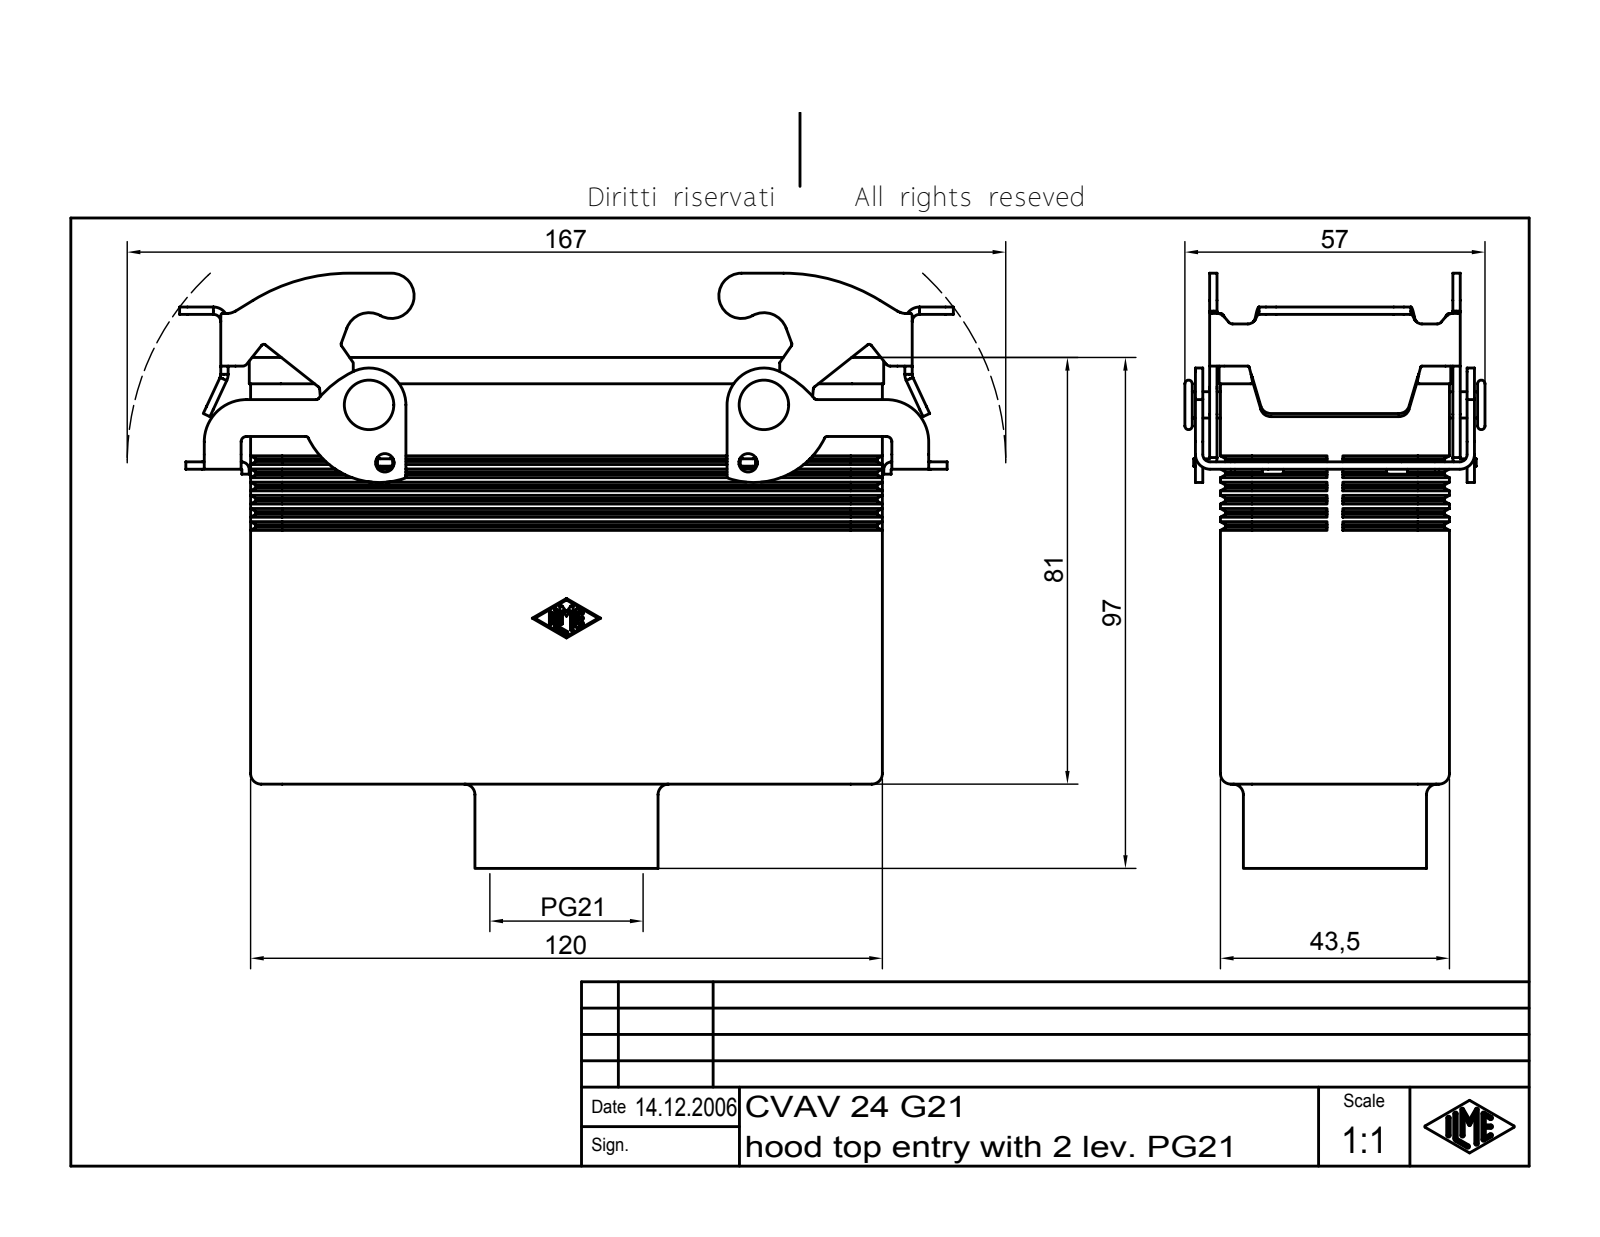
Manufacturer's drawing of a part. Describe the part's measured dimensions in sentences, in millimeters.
The part is named "CVAV 24 G21". Its 3-D file was written by "Autodesk Inventor 7 (AUTOMOTIVE_DESIGN)". It is 3 solids with 834 faces: 246 planar, 204 cylindrical and 384 other. Overall it measures 146.97 by 113 by 57 millimeters. Its volume is 120 834 cubic millimeters and its surface area 81 407 square millimeters. Round holes: 2 of diameter 3.5, 1 of diameter 23.78, 1 of diameter 26.78. Round bosses or shafts: 2 of diameter 5, 2 of diameter 3.2, 1 of diameter 34.78. Partial cylindrical surfaces (rounded edges, fillets, slot ends): 18 of radius 0.5, 16 of radius 0.25, 14 of radius 1, 12 of radius 1.5, 12 of radius 2, 10 of radius 1.4, 10 of radius 2.8, 8 of radius 6. The main face-to-face distances are 3, 40.5, 37.5, 43.5, 1.4, 117, 8.5, 11.75, 120, 11.5. The hole center spacings are 69.
